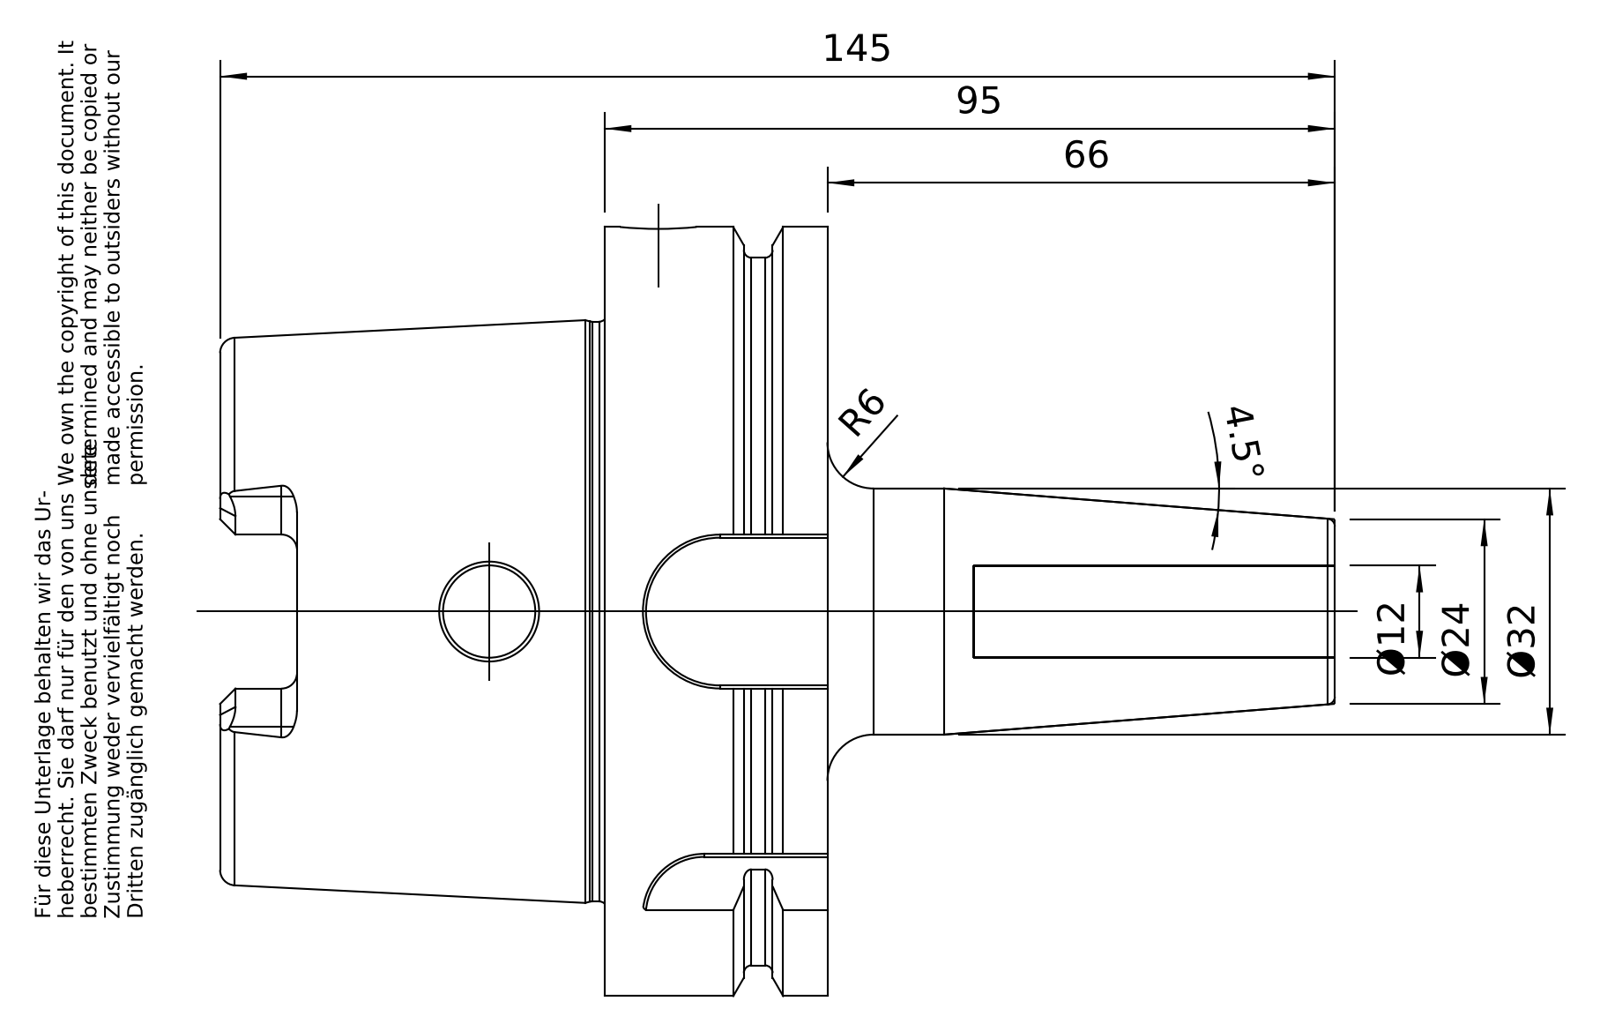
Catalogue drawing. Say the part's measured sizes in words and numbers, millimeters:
The part is named "A100-140-12". Its 3-D file was written by "PRO/ENGINEER BY PARAMETRIC TECHNOLOGY CORPORATION, 2010430 (CONFIG_CONTROL_DESIGN)". It is 1 solid with 174 faces: 50 planar, 51 cylindrical and 73 other. Overall it measures 145 by 100 by 100 millimeters. Its volume is 293 436 cubic millimeters and its surface area 57 396 square millimeters. Round holes: 2 of diameter 12, 1 of diameter 10, 1 of diameter 22.5, 1 of diameter 24, 1 of diameter 24.32, 1 of diameter 24.5, 1 of diameter 53, 1 of diameter 63. Round bosses or shafts: 1 of diameter 100, 1 of diameter 92, 1 of diameter 75.36, 1 of diameter 32. Partial cylindrical surfaces (rounded edges, fillets, slot ends): 6 of radius 2, 4 of radius 5, 1 of radius 8, 1 of radius 10, 1 of radius 11. The main face-to-face distances are 29, 12.5, 16.5, 50, 62.5, 79, 88, 78.5, 28.5, 16.
